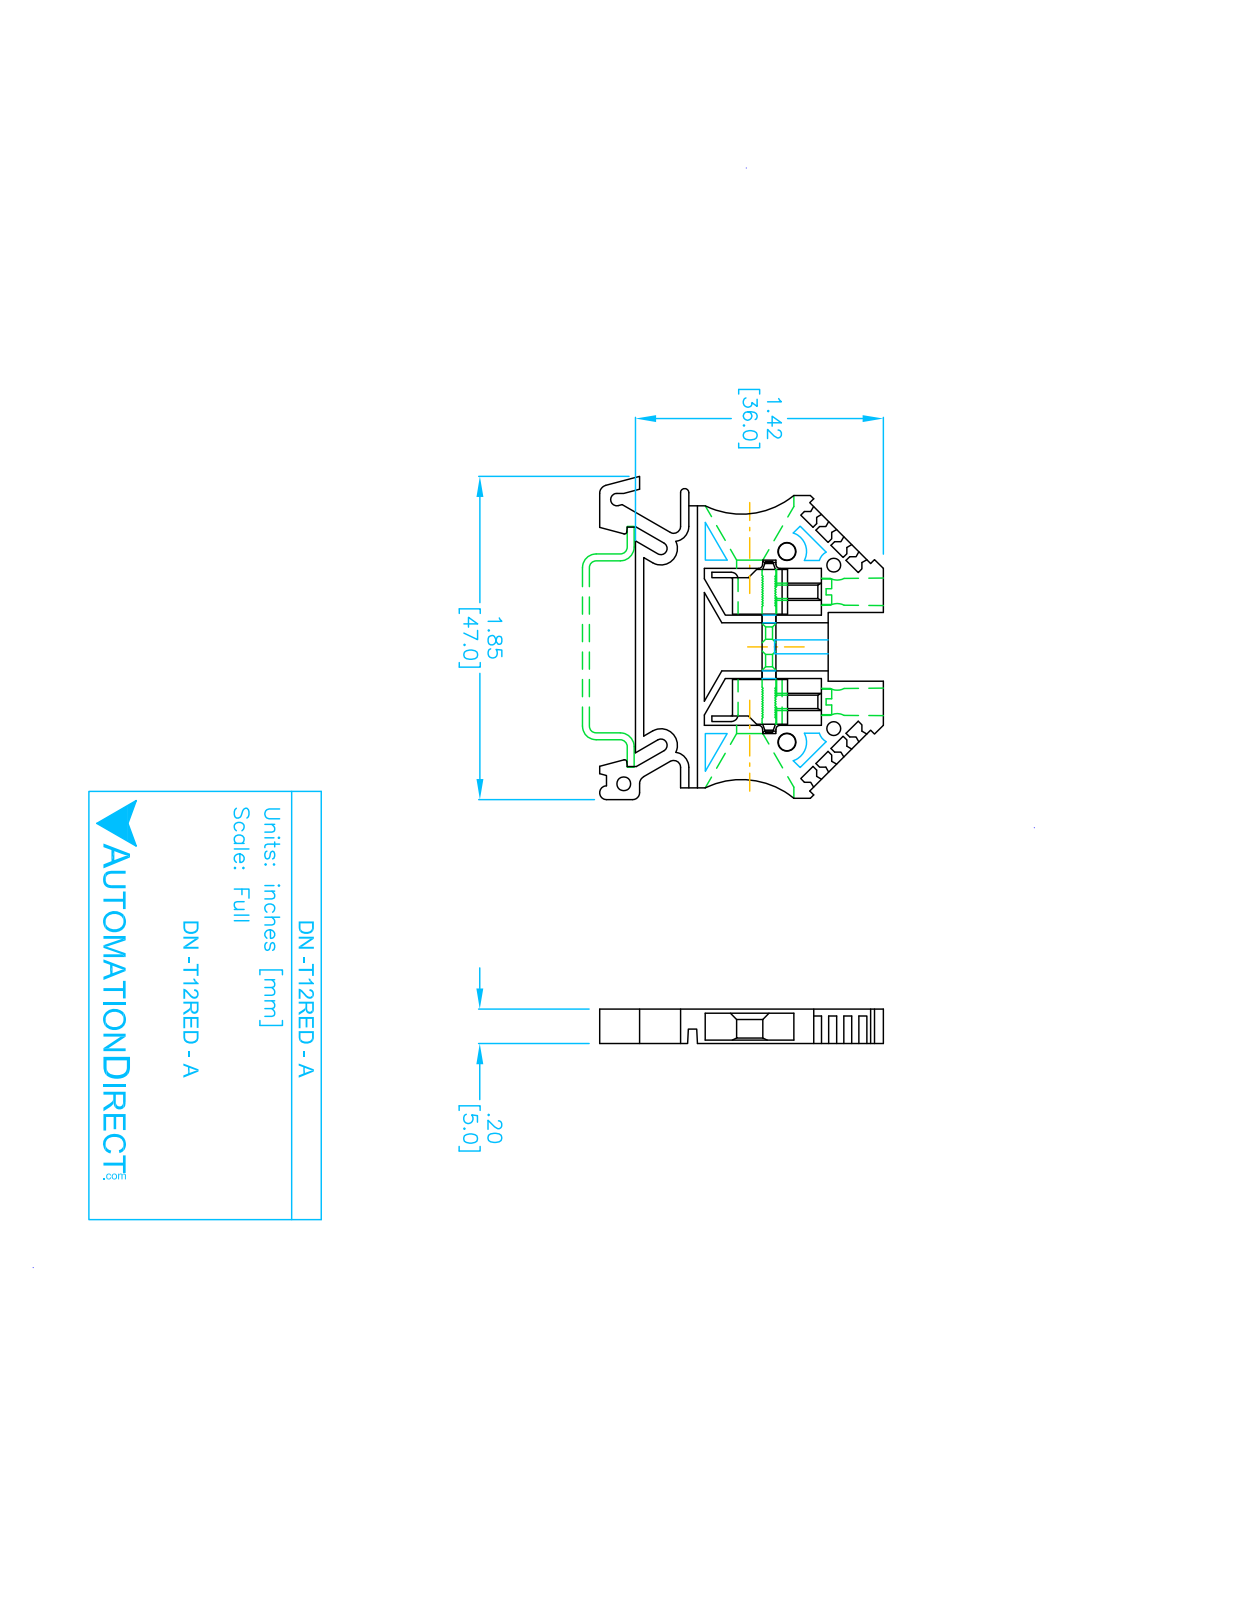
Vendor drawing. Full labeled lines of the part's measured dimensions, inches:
Part name (STEP PRODUCT): DN-T12RED-A
STEP written by: SolidWorks 2017 (AUTOMOTIVE_DESIGN)
Units: inches
Bodies: 1 solid, 169 faces (134 planar, 35 cylindrical, 0 other)
Overall size (bounding box): 1.85 × 1.622 × 0.197
Volume: 0.306 in³ · Surface area: 7.131 in²
Round holes (diameter × count): ⌀0.164 ×2, ⌀0.079 ×1
Partial cylindrical surfaces — rounded edges, fillets, slot ends (radius × count): R0.039 ×4, R0.035 ×3, R0.012 ×2, R0.047 ×2, R0.087 ×2, R0.094 ×2, R0.472 ×2, R0.024 ×1
Main face-to-face distances: 0.189, 0.197, 0.087, 0.02, 0.106, 0.094, 0.114, 0.083, 0.102, 0.354
Hole centre spacings: 0.589
